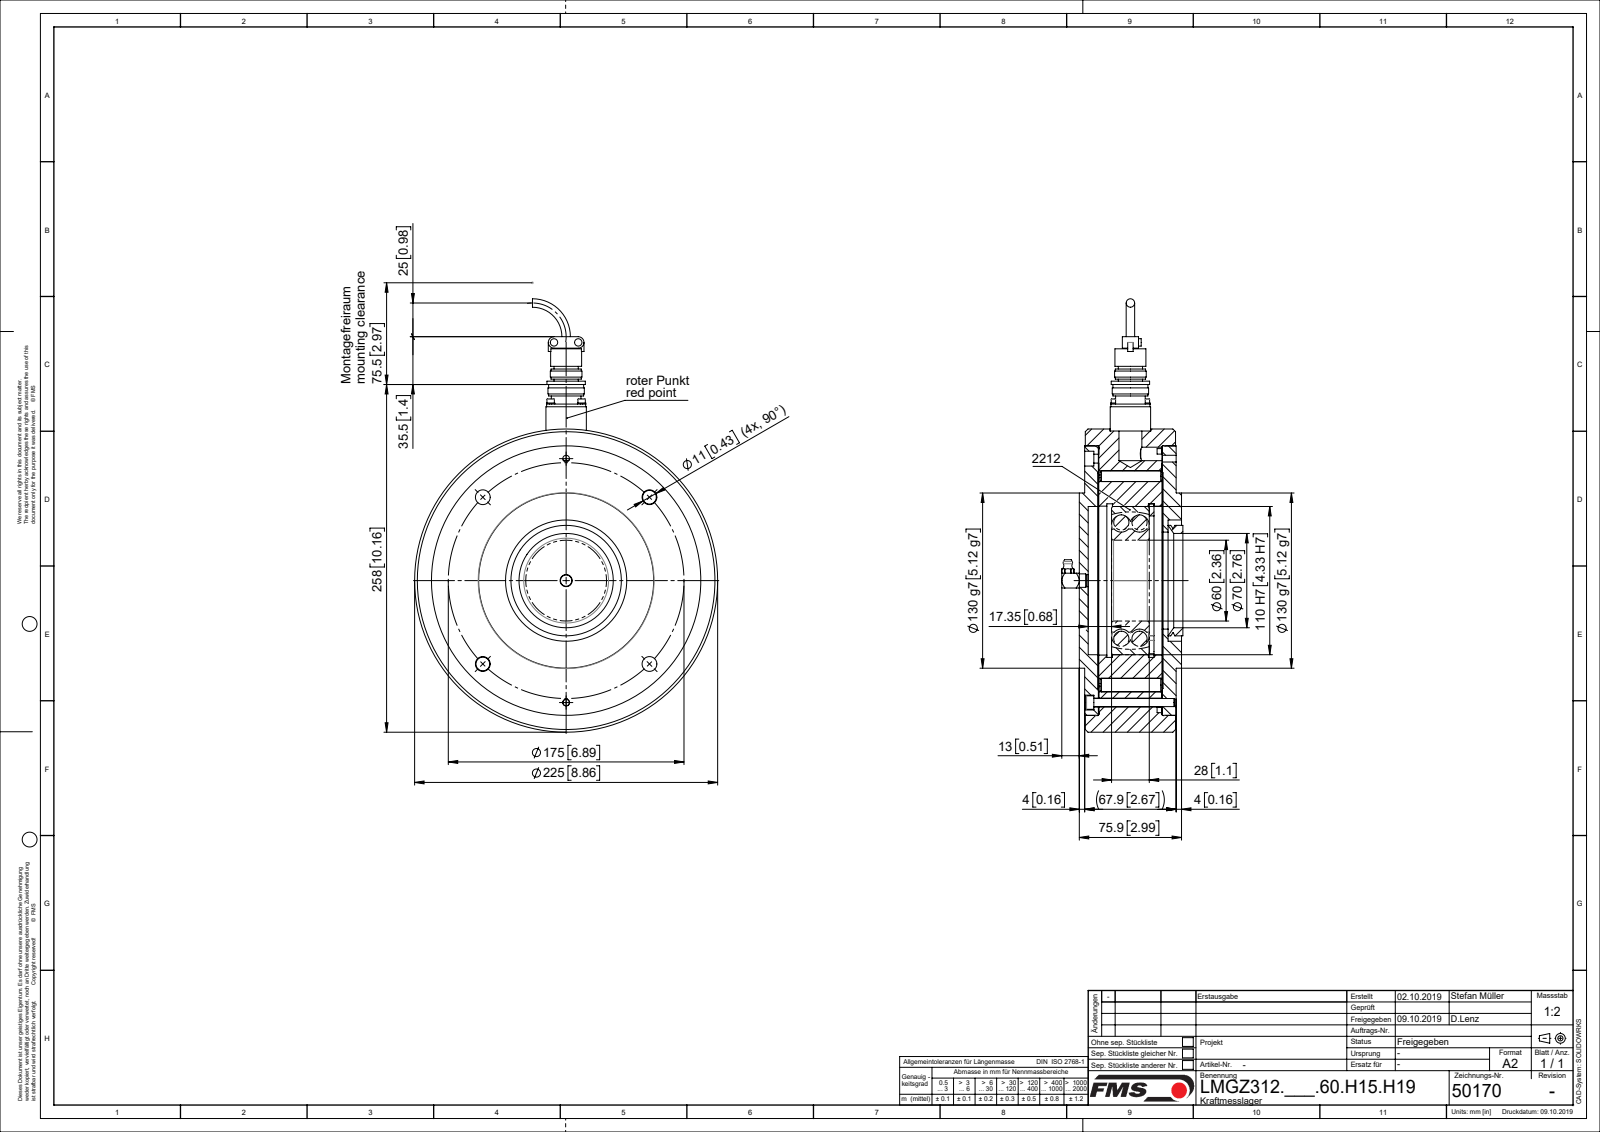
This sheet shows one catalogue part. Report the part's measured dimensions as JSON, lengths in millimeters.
{"part_name": "L50170; L49380; TEIL1; L49026 (+8 more)", "step_written_by": "Mechanical Desktop 2007 (CONFIG_CONTROL_DESIGN)", "units": "millimeters", "bodies": {"solids": 20, "faces": 411, "planar": 119, "cylindrical": 232, "other": 60}, "overall_size": [321.65, 225, 127.8], "volume_mm3": 2379000, "surface_area_mm2": 390674, "round_holes": [[11, 6], [2.6, 4], [3.2, 4], [3.4, 4], [9, 4], [5, 2], [6.6, 2], [8.68, 1], [23, 1], [60, 1], [70, 1], [72, 1]], "round_bosses_or_shafts": [[5.5, 6], [6.2, 4], [3, 4], [2.5, 4], [10, 2], [225, 1], [199, 1], [130, 1]], "partial_cylinders_radius": [[4.25, 2], [81, 1], [86, 1]], "face_to_face_distances": [47.25, 10.2, 10.45, 57.45, 57.7, 47.5, 9.75, 0.5, 48, 9.7], "hole_center_spacings": [16.26, 23, 87.5, 32.53, 68.17, 68.18, 90.5, 123.74]}
